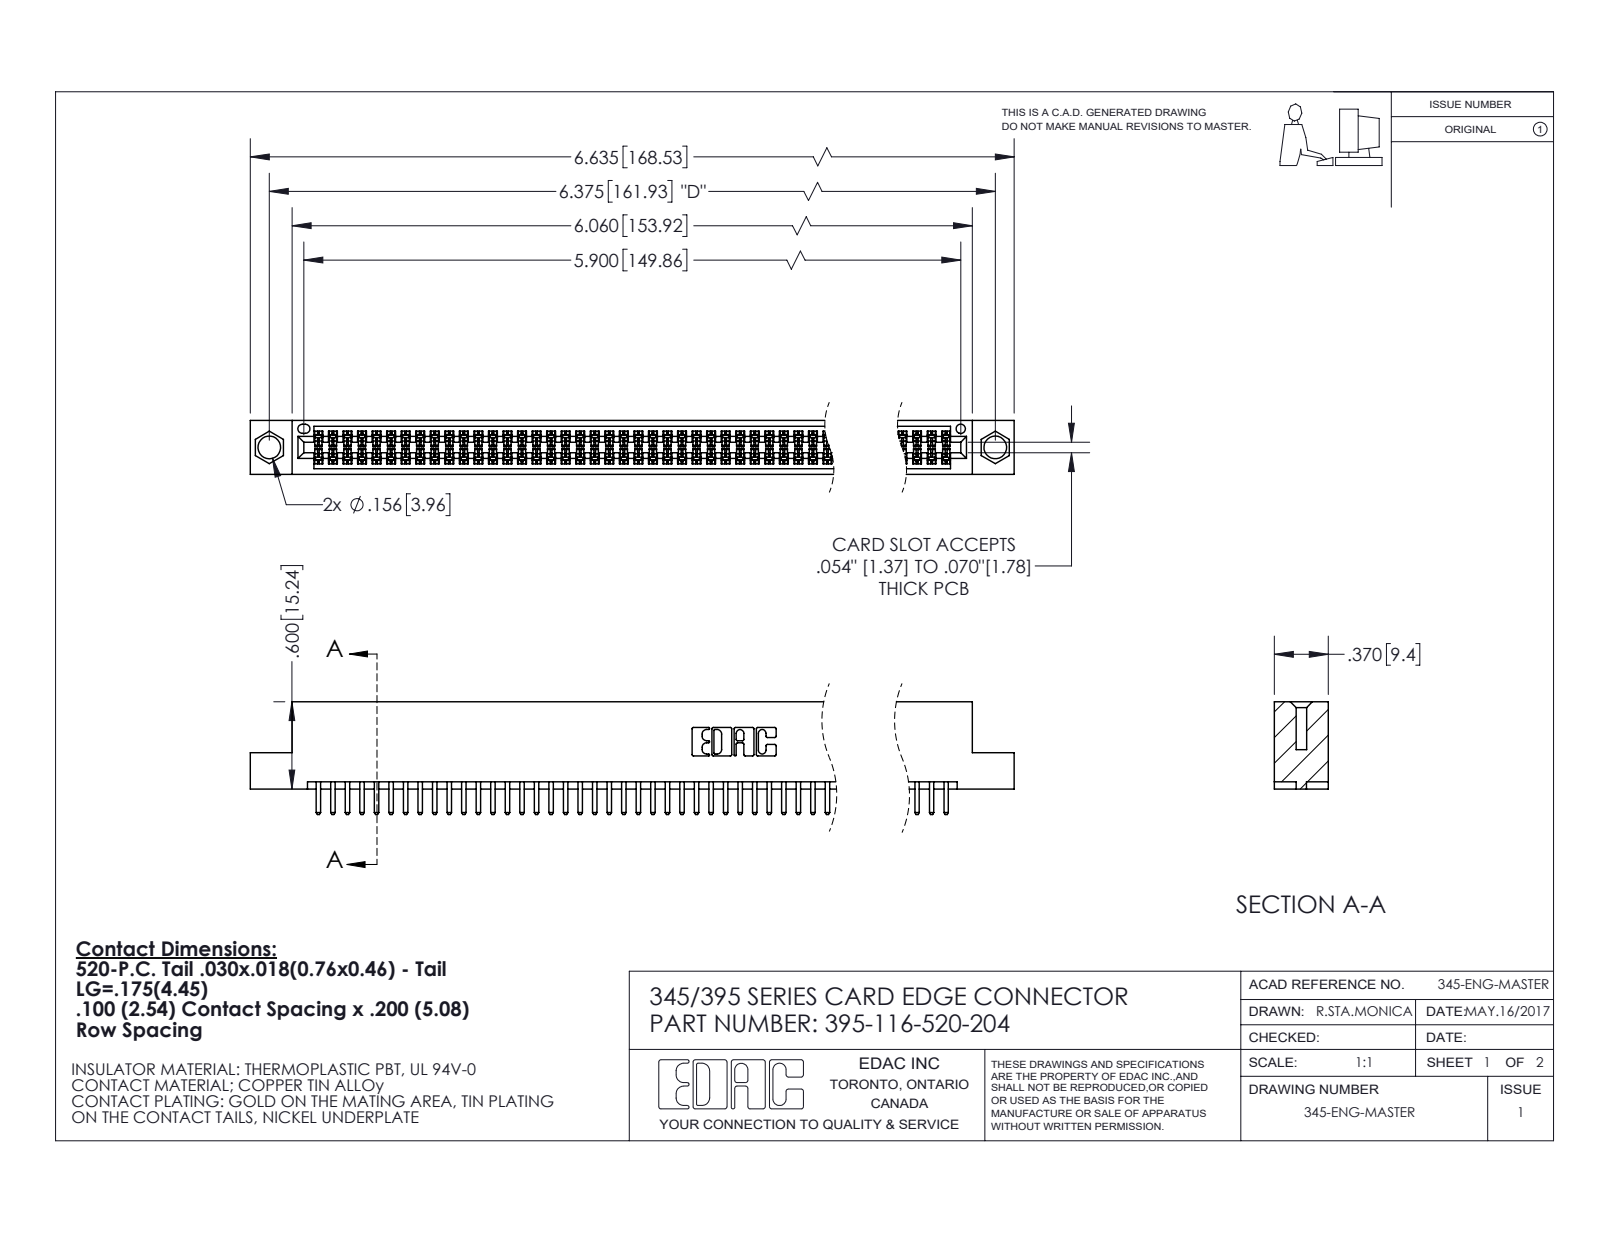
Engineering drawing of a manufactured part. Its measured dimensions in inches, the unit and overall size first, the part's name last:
Units: inches
Overall size (bounding box): 6.635 × 0.775 × 0.37
Round holes (diameter × count): ⌀0.156 ×2, ⌀0.064 ×1
Partial cylindrical surfaces — rounded edges, fillets, slot ends (radius × count): R0.006 ×174, R0.01 ×120, R0.01 ×22, R0.007 ×6, R0.031 ×6, R0.026 ×3, R0.014 ×2, R0.019 ×2
Main face-to-face distances: 0.298, 0.072, 0.2, 0.37, 0.098, 0.272, 0.025, 0.225, 0.022, 0.072
Hole centre spacings: 0.27, 6.139, 6.375
Volume: 0.999 in³ · Surface area: 37.57 in²
Bodies: 117 solids, 6404 faces (4154 planar, 2250 cylindrical, 0 other)
Part name (STEP PRODUCT): 345-292-001_345-293-120; 395-116-520-204; 345 Part_Flush Mounting Lugs - 0.156 Dia-TI
STEP written by: SolidWorks 2020 (CONFIG_CONTROL_DESIGN)
